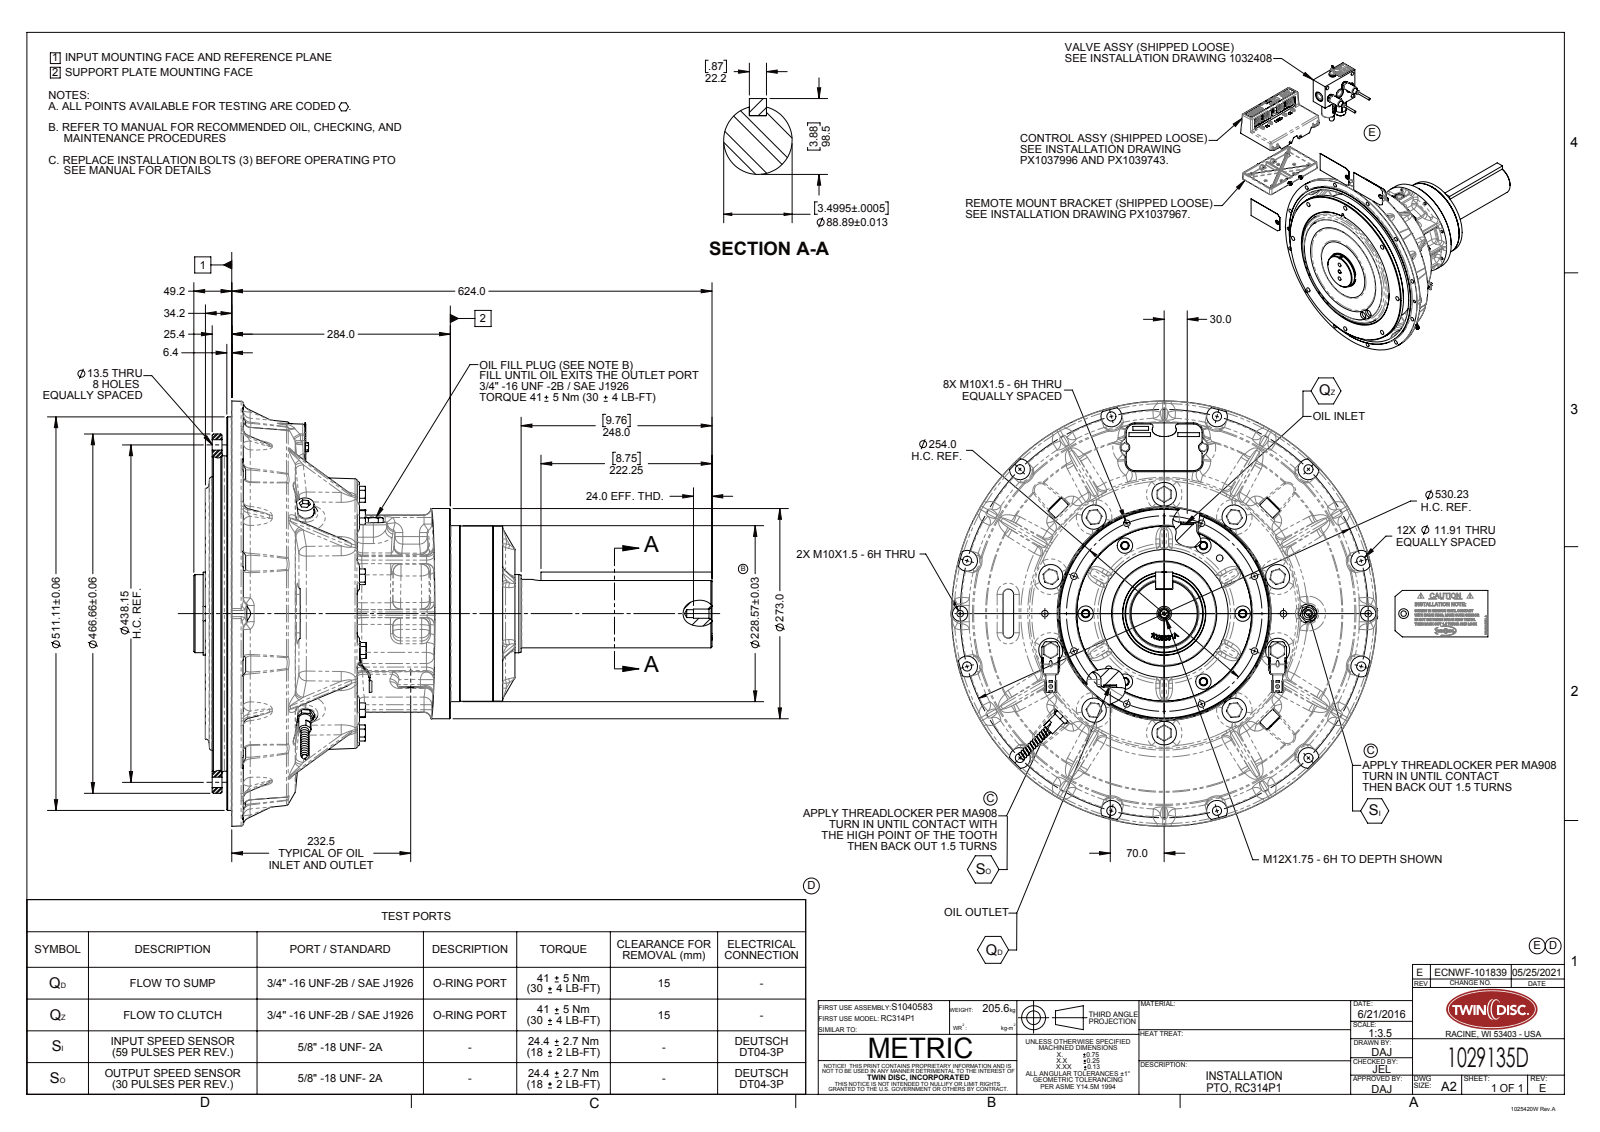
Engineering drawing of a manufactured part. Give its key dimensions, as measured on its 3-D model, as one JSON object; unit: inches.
{"part_name": "1029135D", "step_written_by": "SolidWorks 2019 (AUTOMOTIVE_DESIGN)", "units": "inches", "bodies": {"solids": 0, "faces": 1802, "planar": 415, "cylindrical": 357, "other": 1030}, "overall_size": [26.504, 21.813, 21.744], "round_holes": [[0.335, 14], [0.469, 12], [0.531, 8], [0.472, 3], [1.188, 3], [0.75, 2], [0.787, 2], [0.875, 2], [0.425, 1], [1, 1], [10.945, 1], [14.75, 1]], "round_bosses_or_shafts": [[0.625, 2], [0.315, 2], [20.123, 1], [18.373, 1], [10.866, 1], [10.748, 1], [8.999, 1], [8.957, 1]], "partial_cylinders_radius": [[0.394, 93], [0.118, 74], [0.197, 12], [0.531, 12], [0.06, 8], [0.5, 5], [0.03, 4], [0.05, 4]], "face_to_face_distances": [0.748, 1, 0.252, 1.35, 0.602, 0.35, 1.291, 0.543, 0.291, 0.059], "hole_center_spacings": [8.148, 4.439, 13.382, 11.506, 3.827, 5, 6.601, 7.071]}
